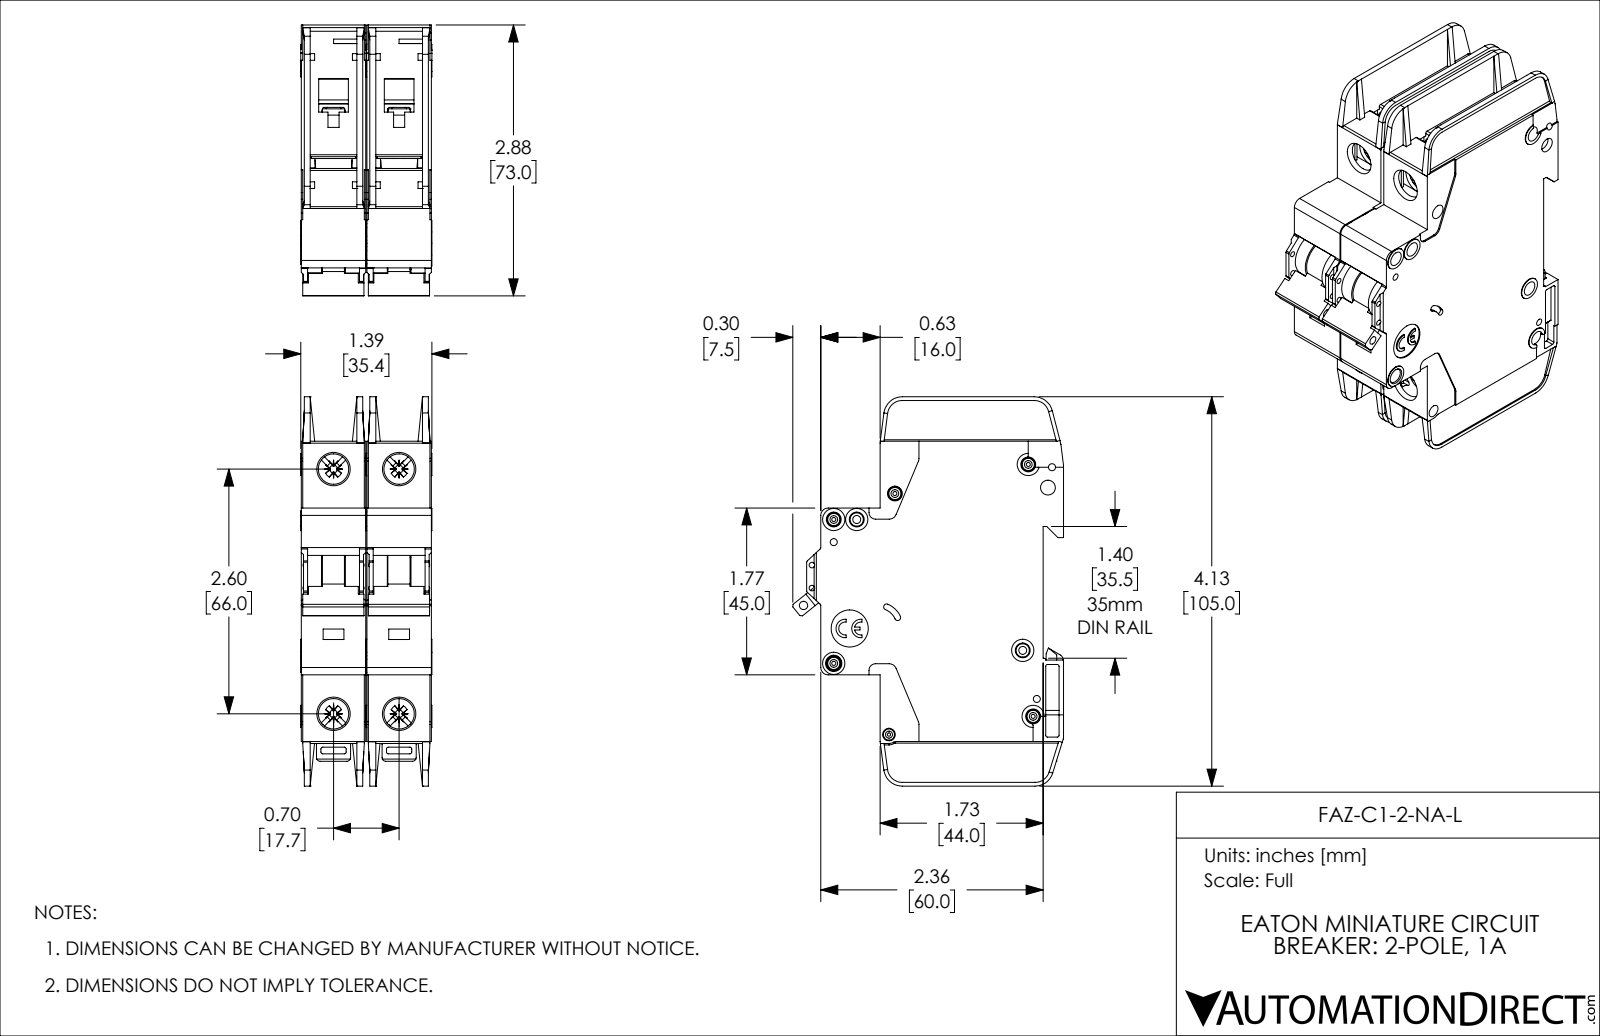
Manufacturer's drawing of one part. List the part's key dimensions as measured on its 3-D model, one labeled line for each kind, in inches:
Part name (STEP PRODUCT): FAZ-C1-2-NA-L
STEP written by: SolidWorks 2019 (AUTOMOTIVE_DESIGN)
Units: inches
Bodies: 2 solids, 2254 faces (1342 planar, 714 cylindrical, 198 other)
Overall size (bounding box): 4.134 × 2.876 × 1.394
Volume: 9.365 in³ · Surface area: 82.01 in²
Round holes (diameter × count): ⌀0.157 ×8, ⌀0.043 ×5, ⌀0.075 ×4, ⌀0.323 ×4, ⌀0.059 ×2, ⌀0.085 ×2, ⌀0.035 ×1, ⌀0.089 ×1, ⌀0.098 ×1, ⌀0.134 ×1, ⌀0.394 ×1
Round bosses / shafts (diameter × count): ⌀0.13 ×5, ⌀0.236 ×4, ⌀0.118 ×3, ⌀0.098 ×2
Partial cylindrical surfaces — rounded edges, fillets, slot ends (radius × count): R0.02 ×57, R0.016 ×20, R0.039 ×14, R0.079 ×10, R0.043 ×8, R0.008 ×5, R0.197 ×5, R0.01 ×4
Main face-to-face distances: 0.697, 0.047, 0.685, 0.591, 0.094, 0.638, 0.543, 1.382, 0.744, 0.65
Hole centre spacings: 0.244, 0.537, 0.697, 0.87, 2.598, 2.69, 0.189, 0.199
